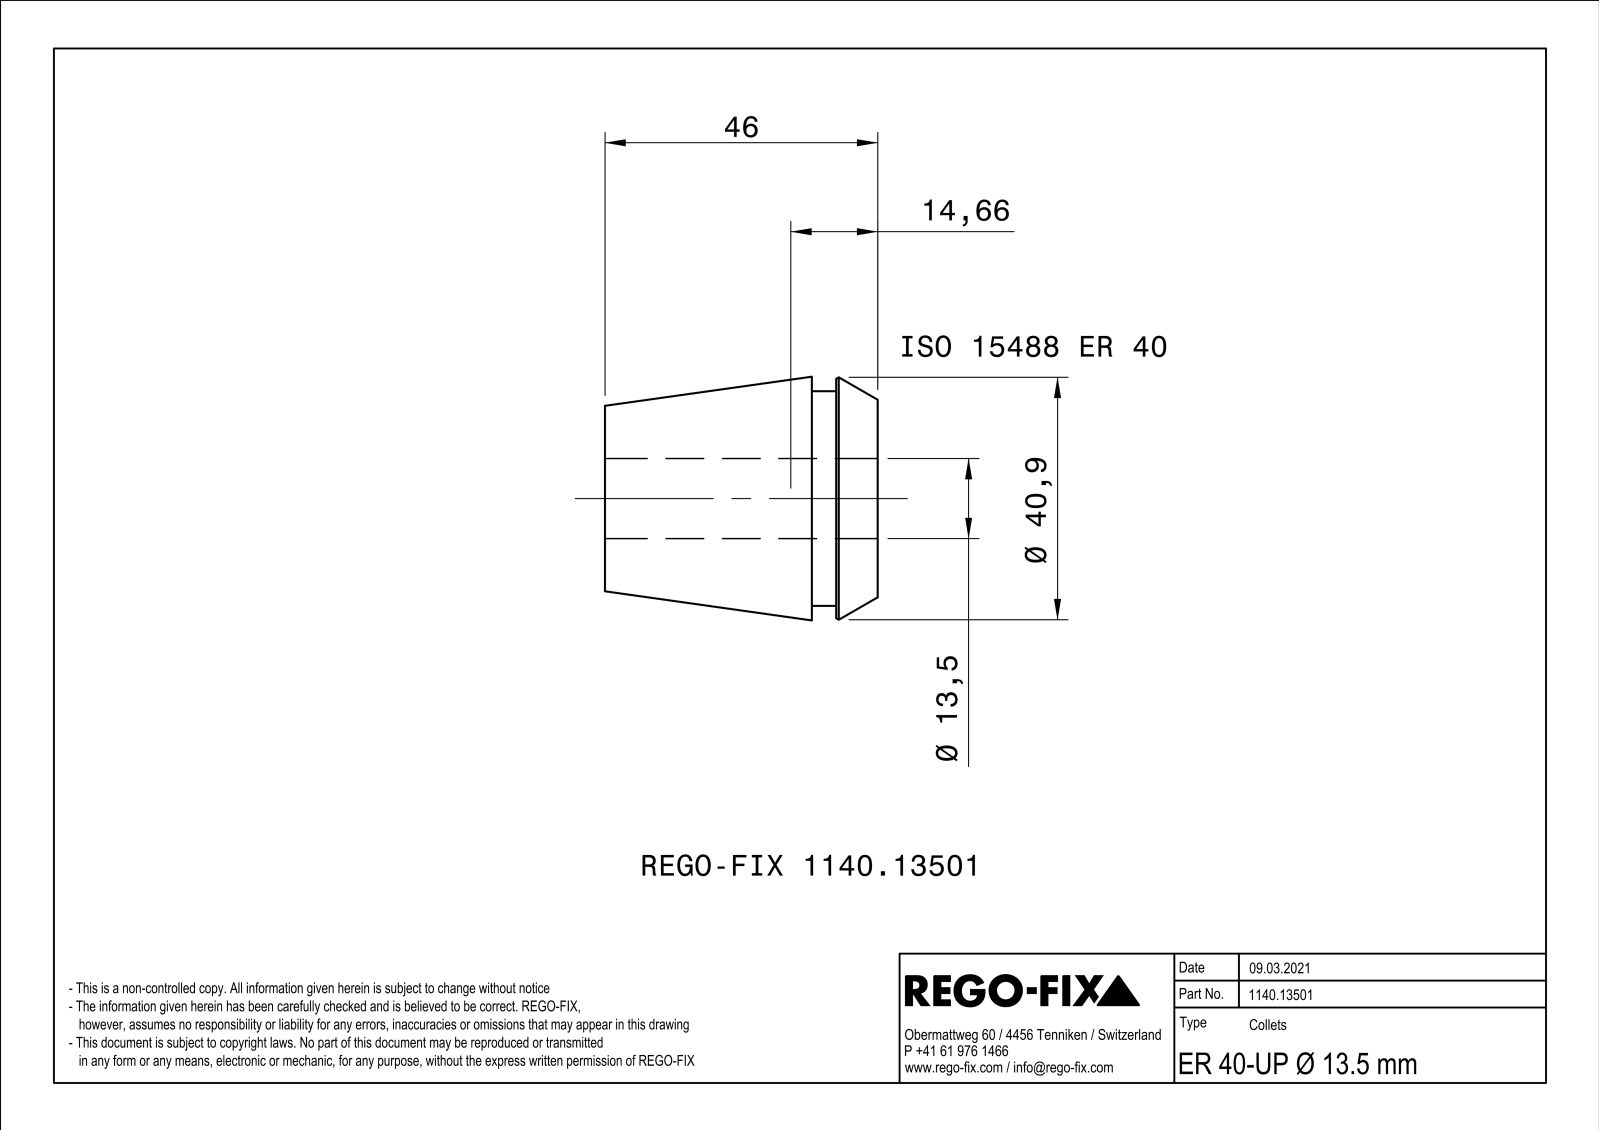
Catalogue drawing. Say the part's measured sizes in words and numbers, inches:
The part is named "NOCUT". Its 3-D file was written by "SIEMENS PLM Software Solid Edge ST10 (AUTOMOTIVE_DESIGN)". It is 1 solid with 177 faces: 88 planar, 9 cylindrical and 80 other. Overall it measures 1.811 by 1.614 by 1.614 inches. Its volume is 2.064 cubic inches and its surface area 35.2 square inches. Round holes: 1 of diameter 0.531. Round bosses or shafts: 1 of diameter 1.425. The main face-to-face distances are 0.039, 1.811, 0.437, 1.374, 0.276, 0.161, 1.535, 0.295, 0.02, 0.142.
